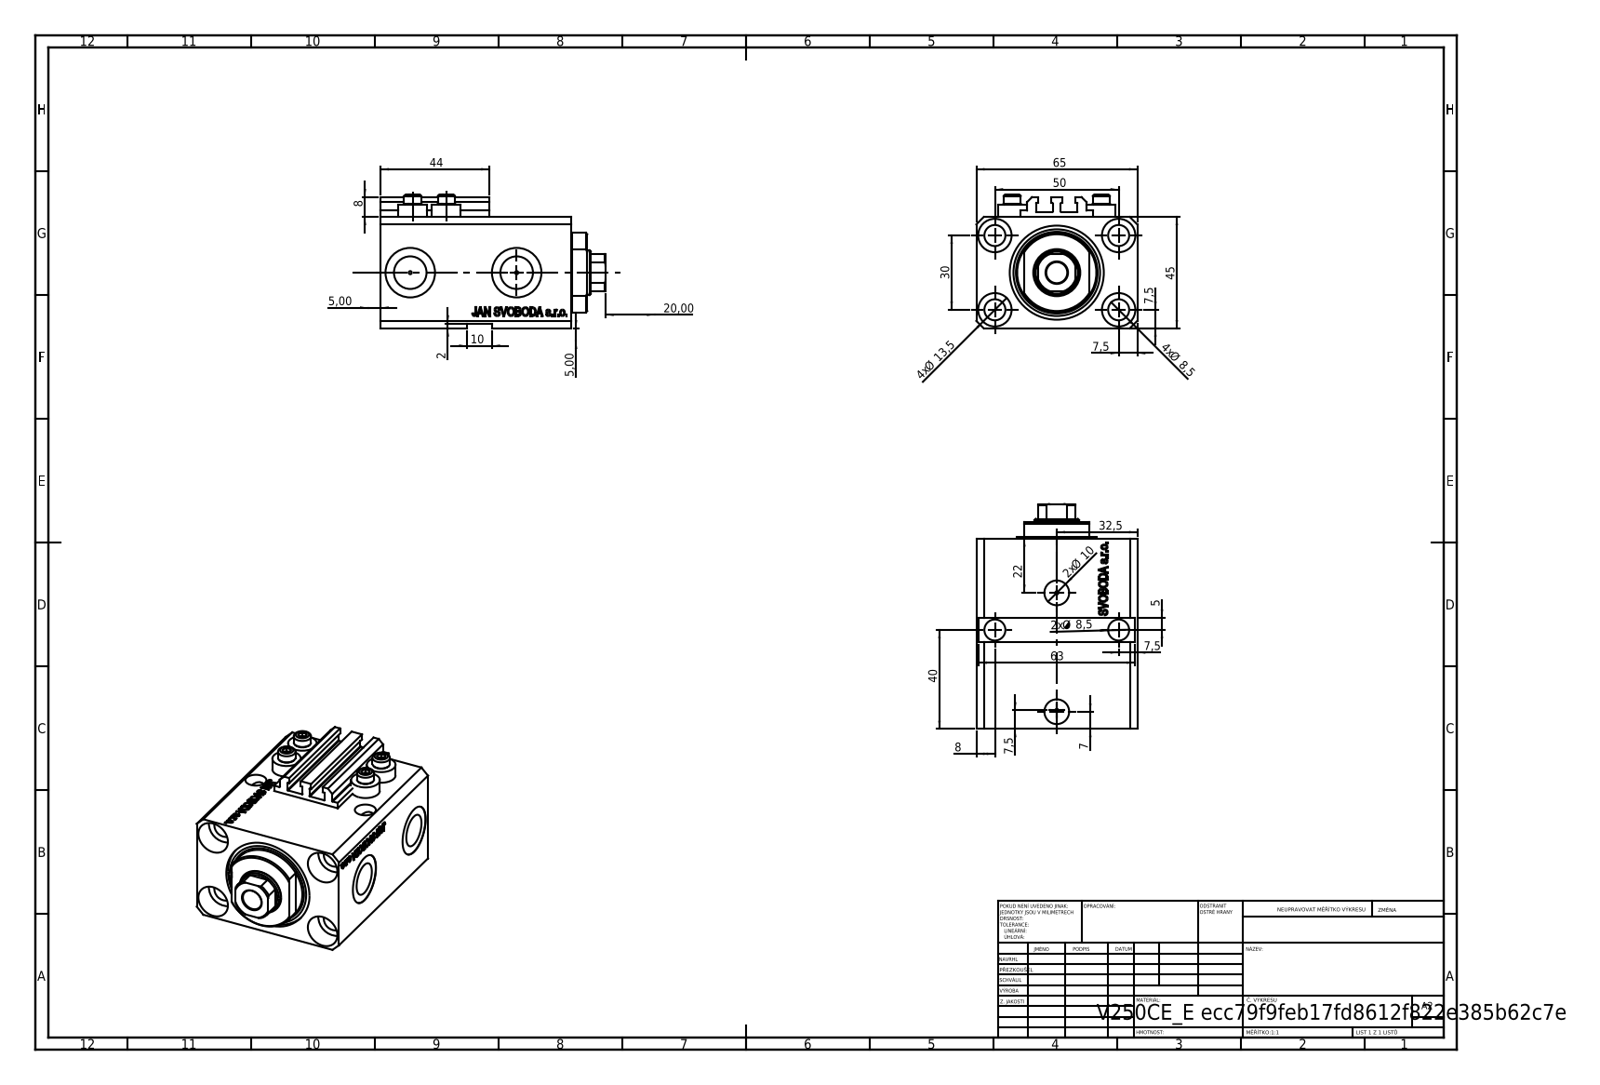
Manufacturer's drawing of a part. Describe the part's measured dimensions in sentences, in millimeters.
The part is named "V250CE_E_Body; ALLEN BOLT V250CE; V250CE_C_VCP; V250CE_VC_E". Its 3-D file was written by "SolidWorks 2019 (CONFIG_CONTROL_DESIGN)". It is 8 solids with 1083 faces: 515 planar, 138 cylindrical and 430 other. Overall it measures 90.9 by 65 by 54 millimeters. Its volume is 196 157 cubic millimeters and its surface area 62 402 square millimeters. Round holes: 7 of diameter 8.5, 4 of diameter 1.25, 4 of diameter 4, 4 of diameter 13.5, 2 of diameter 10, 2 of diameter 13.16, 2 of diameter 20, 1 of diameter 18, 1 of diameter 25, 1 of diameter 38. Round bosses or shafts: 4 of diameter 11.6, 4 of diameter 7. Partial cylindrical surfaces (rounded edges, fillets, slot ends): 10 of radius 0.2, 1 of radius 8.5, 1 of radius 16. The main face-to-face distances are 45, 65, 51.9, 77, 25.1, 2, 6.9, 70.1, 3, 9. The hole center spacings are 29.15, 50, 13.6, 15.12, 18.81, 18.97, 26.22, 26.61.
